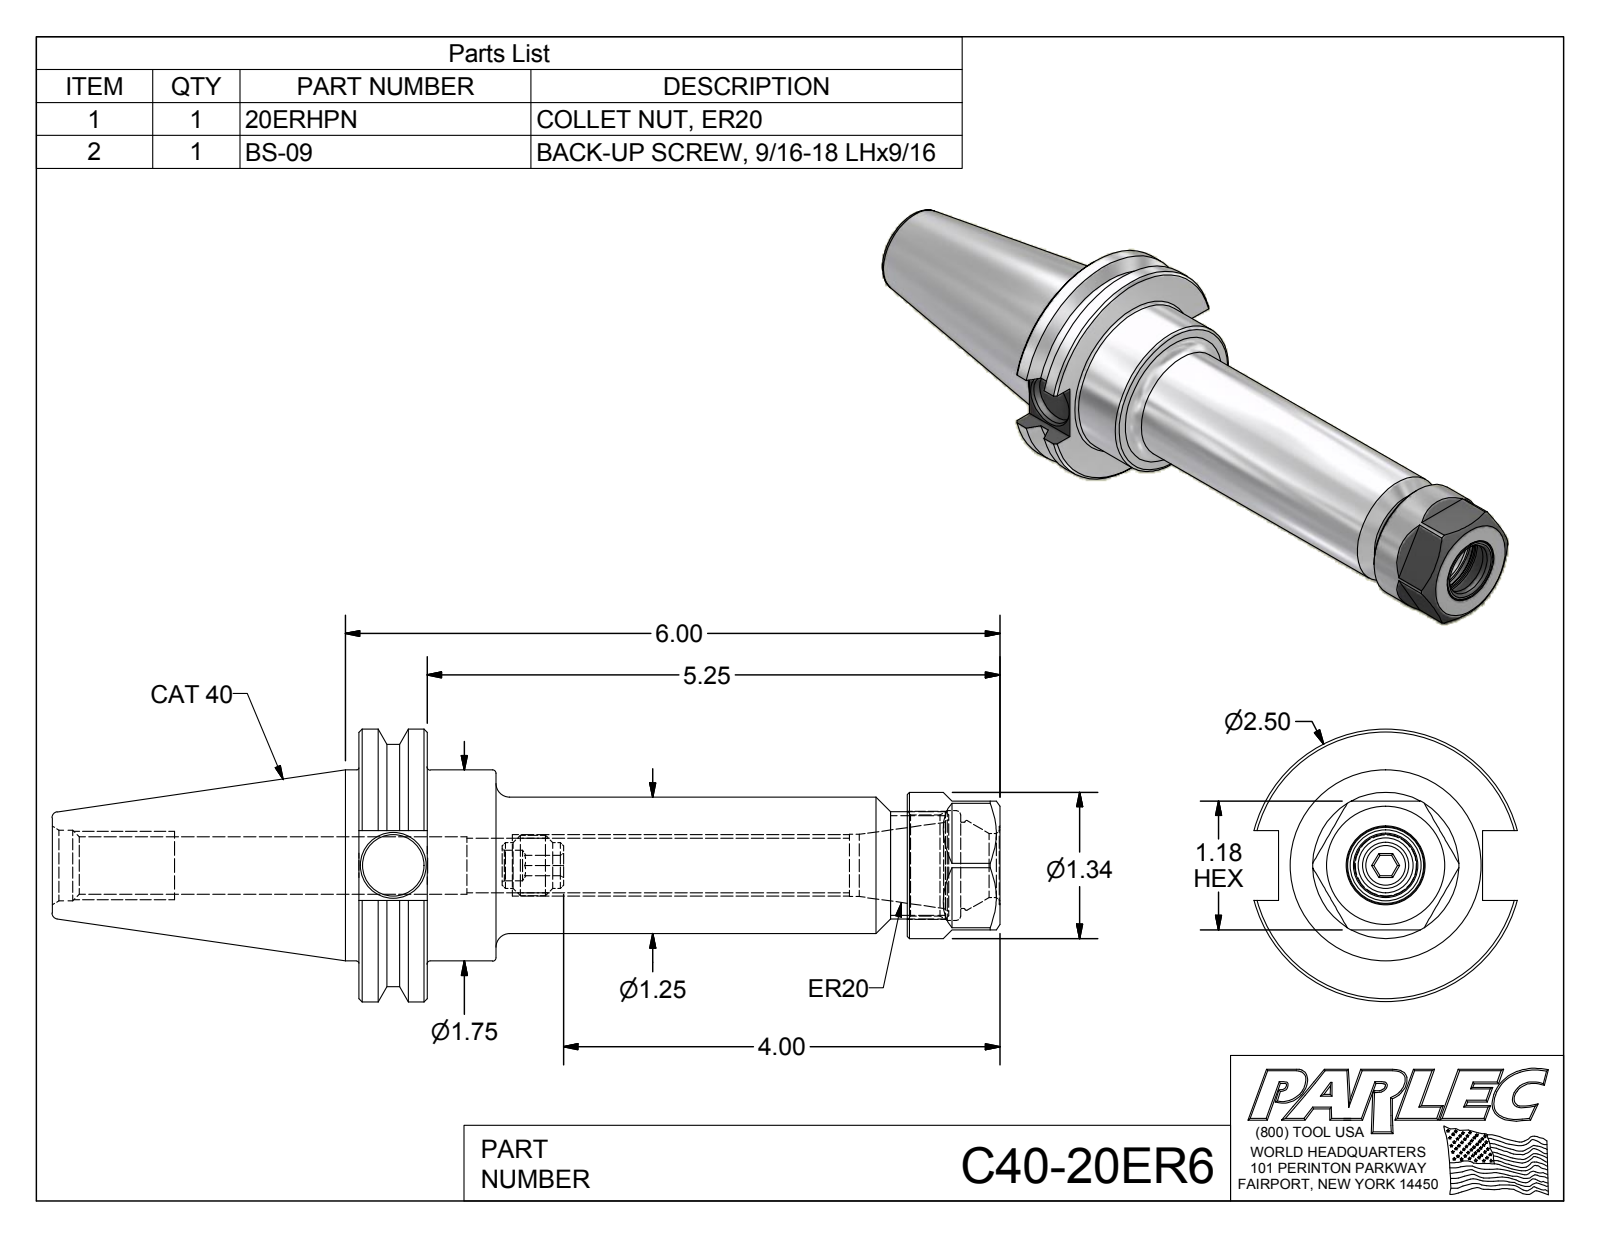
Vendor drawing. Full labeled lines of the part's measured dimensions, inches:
Part name (STEP PRODUCT): C40-20ER6; C40-20ER6-1; 20ERHPN; BS-09
STEP written by: Autodesk Inventor 2012 (AUTOMOTIVE_DESIGN)
Units: inches
Bodies: 3 solids, 107 faces (43 planar, 24 cylindrical, 40 other)
Overall size (bounding box): 8.688 × 2.5 × 2.417
Volume: 12.06 in³ · Surface area: 66.55 in²
Round holes (diameter × count): ⌀0.281 ×1, ⌀0.502 ×1, ⌀0.527 ×1, ⌀0.563 ×1, ⌀0.57 ×1, ⌀0.587 ×1, ⌀0.648 ×1, ⌀0.79 ×1, ⌀0.926 ×1, ⌀1.005 ×1
Round bosses / shafts (diameter × count): ⌀2.5 ×1, ⌀2.219 ×1, ⌀1.75 ×1, ⌀1.34 ×1, ⌀1.25 ×1, ⌀0.984 ×1, ⌀0.555 ×1, ⌀0.422 ×1
Main face-to-face distances: 0.625, 1.18, 5.025, 4.4, 5.875, 5.25, 0.85, 0.27, 0.91, 1.255
